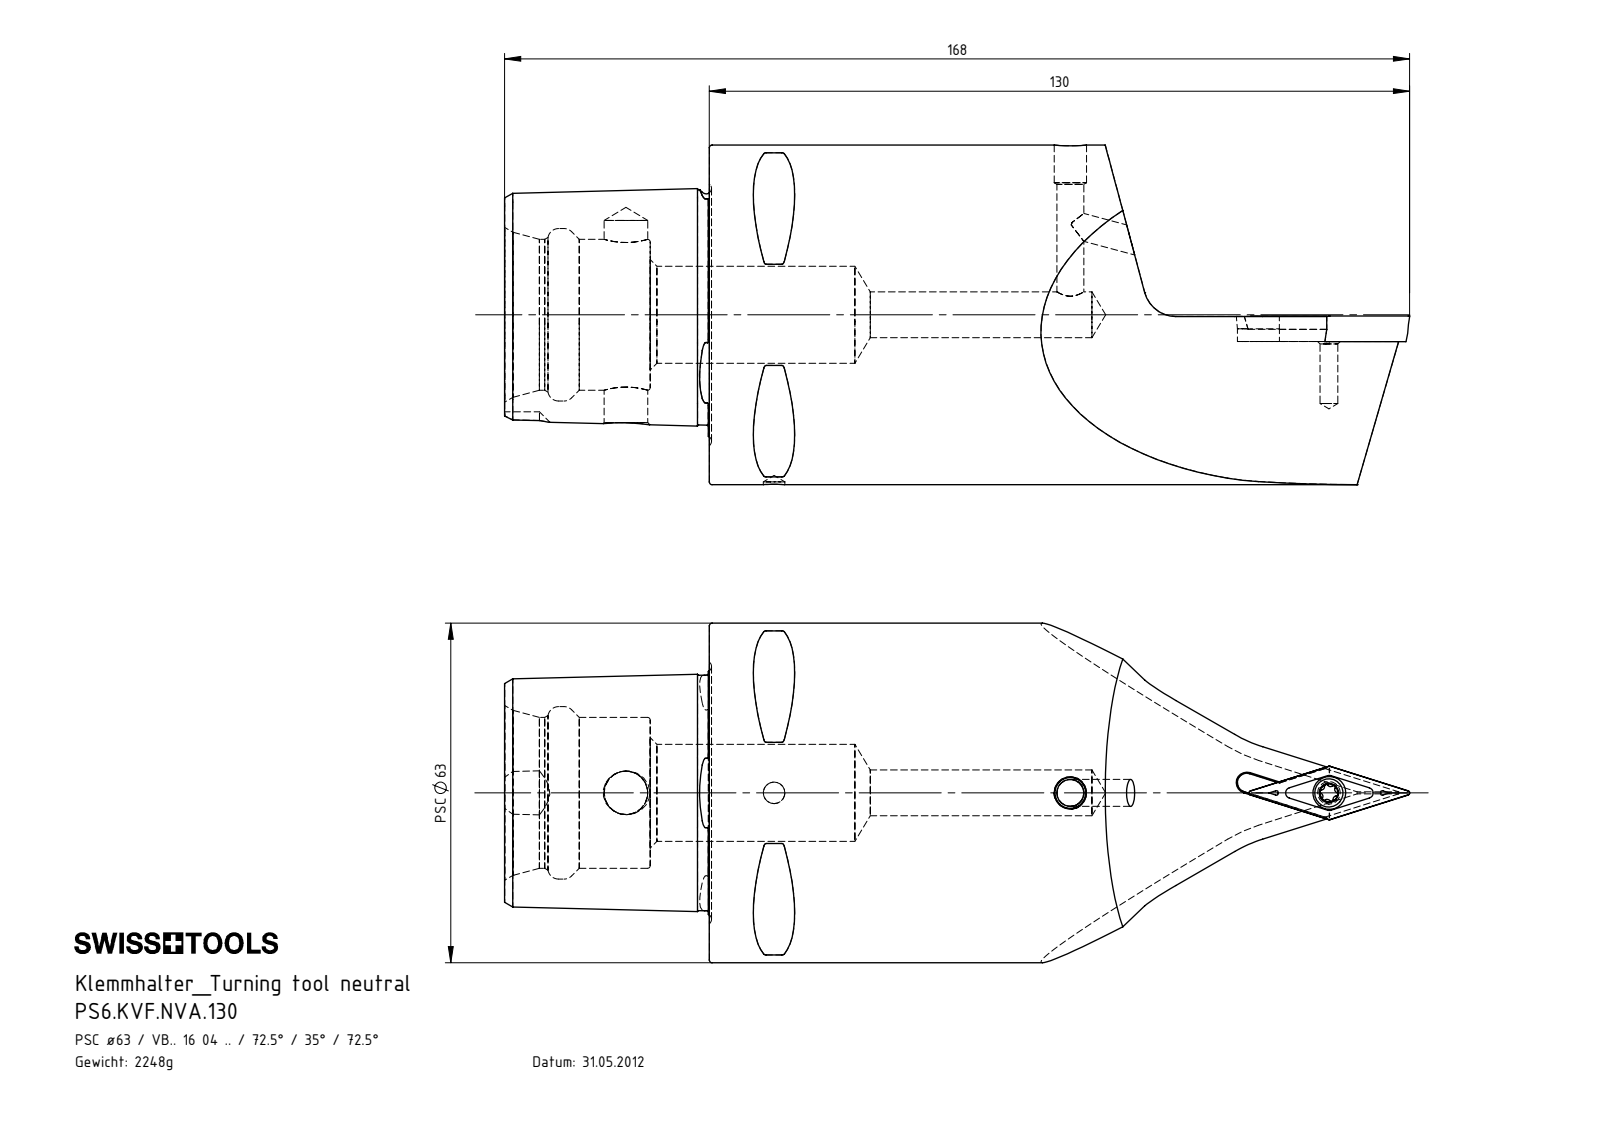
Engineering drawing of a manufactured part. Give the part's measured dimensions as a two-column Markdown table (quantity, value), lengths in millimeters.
| quantity | value |
| --- | --- |
| part name | WCB-ER2.001.009_A; KVT_MB_600_060; VBMT160404; PS6-KVF.NVA.130_A (+1 more) |
| STEP written by | SolidWorks 2017 (AUTOMOTIVE_DESIGN) |
| units | millimeters |
| bodies | 5 solids, 276 faces (56 planar, 71 cylindrical, 149 other) |
| overall size | 168 × 63 × 63 |
| volume | 286 671 mm³ |
| surface area | 37 414 mm² |
| round holes (diameter × count) | 5 × 2, 3.3 × 1, 4 × 1, 4.4 × 1, 6.1 × 1, 8.1 × 1, 8.5 × 1, 18 × 1, 28 × 1, 32 × 1 |
| round bosses / shafts (diameter × count) | 63 × 1, 6 × 1, 5.25 × 1, 4 × 1 |
| partial cylindrical surfaces (radius × count) | 0.5 × 8, 0.34 × 6, 0.59 × 6, 0.15 × 2, 0.8 × 2, 6 × 2, 1.75 × 1 |
| main face-to-face distances | 38, 24.88, 4.66, 27, 11, 55.8, 37.8, 10.8, 4.76, 29.16 |
| hole center spacings | 27.5, 47.99, 48.09, 55, 82.5, 102.99, 103.09, 130.49 |
